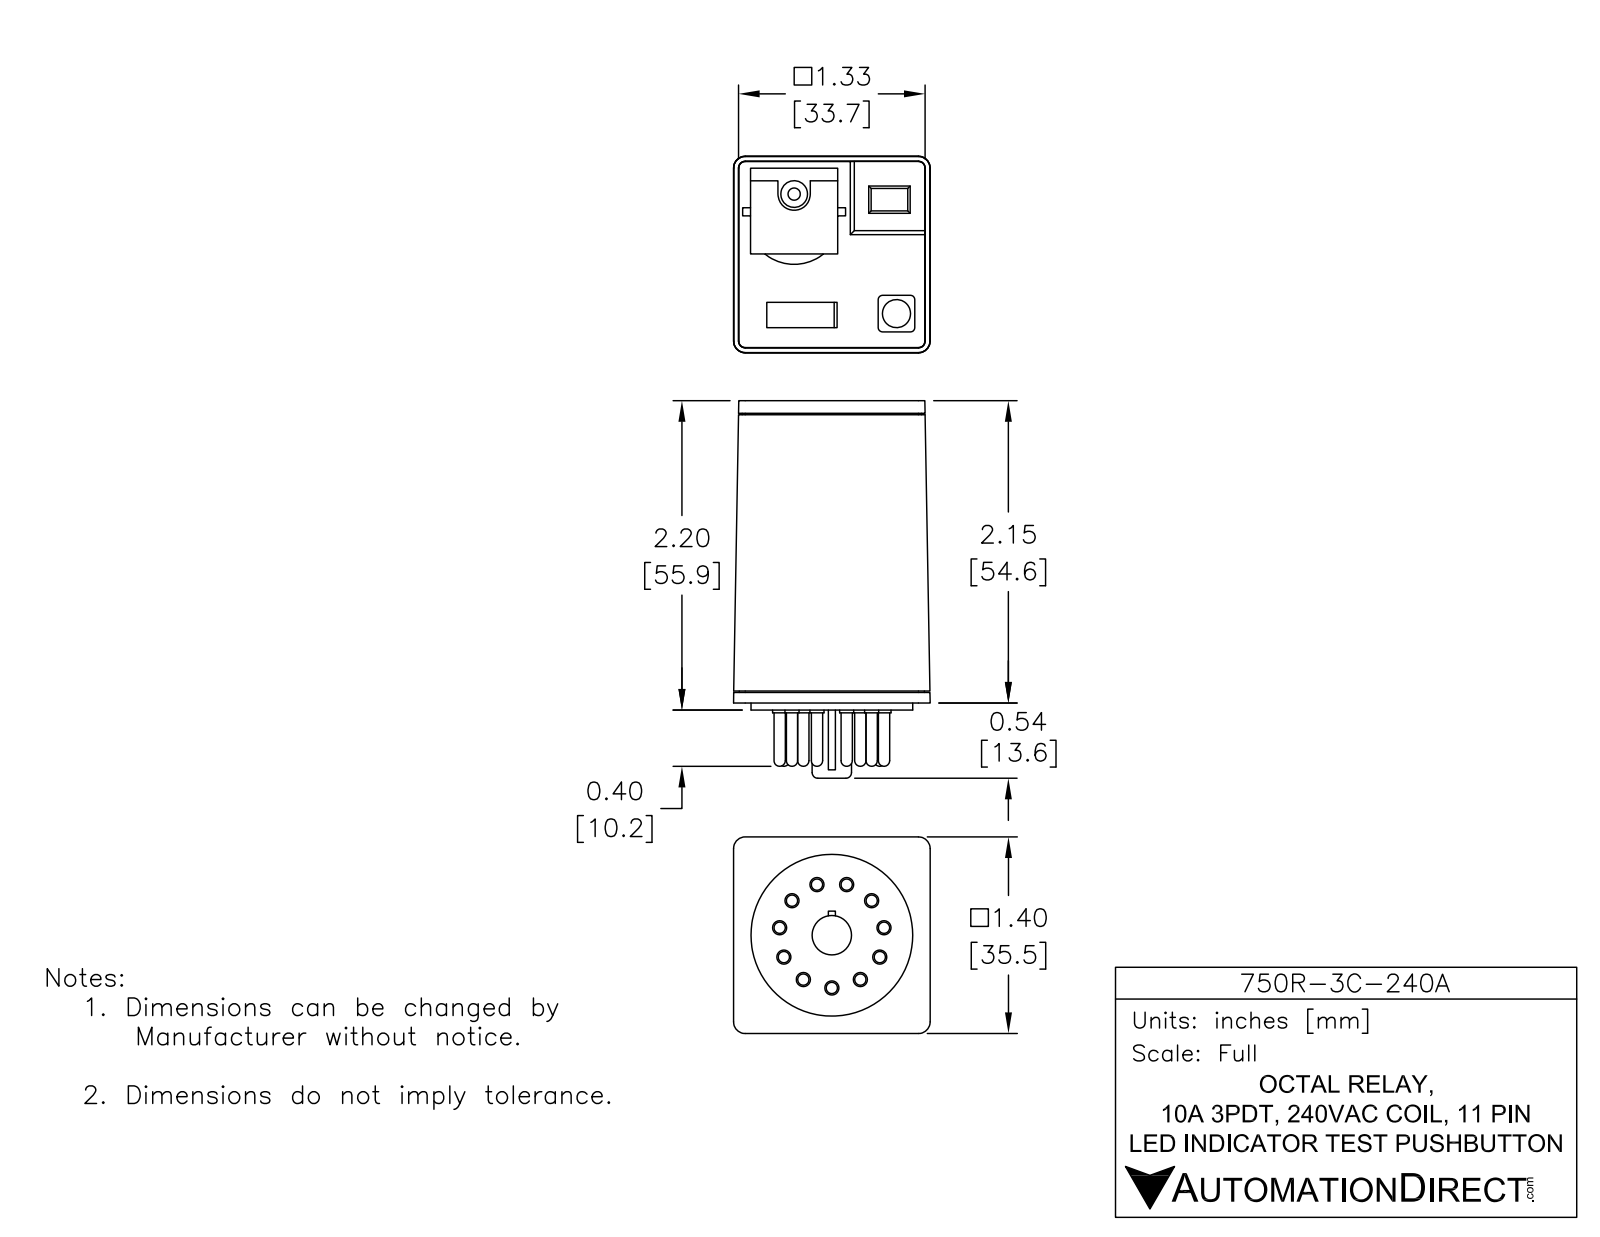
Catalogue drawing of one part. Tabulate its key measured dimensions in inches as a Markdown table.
| quantity | value |
| --- | --- |
| part name | 750R-3C-240A |
| STEP written by | SolidWorks 2014 (AUTOMOTIVE_DESIGN) |
| units | inches |
| bodies | 1 solid, 180 faces (93 planar, 62 cylindrical, 25 other) |
| overall size | 2.685 × 1.398 × 1.398 |
| volume | 4.056 in³ |
| surface area | 17.68 in² |
| round holes (diameter × count) | 0.087 × 1, 0.2 × 1 |
| round bosses / shafts (diameter × count) | 0.1 × 11, 0.08 × 11, 1.15 × 1, 0.28 × 1, 0.19 × 1 |
| partial cylindrical surfaces (radius × count) | 0.03 × 4, 0.115 × 1, 0.33 × 1 |
| main face-to-face distances | 0.05, 2.15, 2.2, 2.11, 0.04, 2.19, 2.14, 0.085, 0.03, 2.16 |
| hole center spacings | 1.119 |
